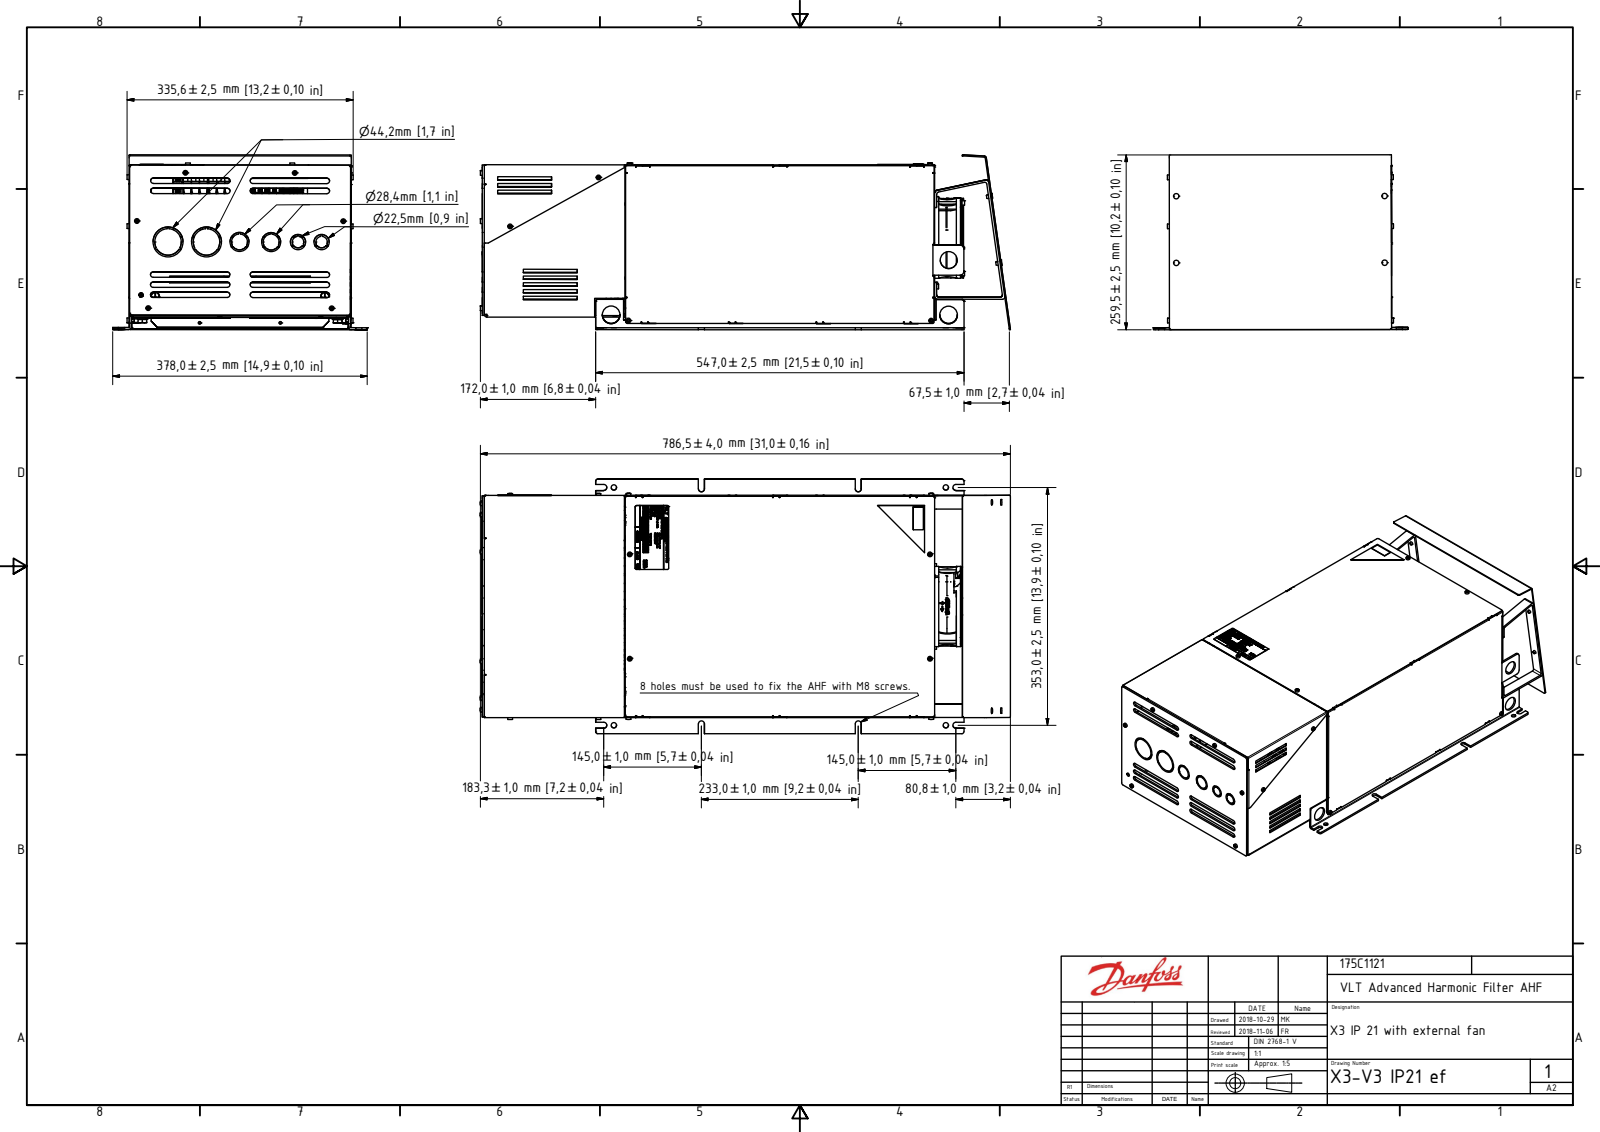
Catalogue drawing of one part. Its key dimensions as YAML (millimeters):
part_name: "X3.3 IP21 ef"
step_written_by: "Autodesk Inventor 2018 (AUTOMOTIVE_DESIGN)"
units: millimeters
bodies: {solids: 24, faces: 13044, planar: 8083, cylindrical: 3125, other: 1836}
overall_size: [787.14, 378, 259.83]
volume: 518530
surface_area: 2686000
round_holes:
  - {diameter: 3.24, count: 21}
  - {diameter: 4, count: 20}
  - {diameter: 6.8, count: 17}
  - {diameter: 8.4, count: 15}
  - {diameter: 3.6, count: 14}
  - {diameter: 8.5, count: 13}
  - {diameter: 5, count: 12}
  - {diameter: 5.5, count: 12}
  - {diameter: 6.32, count: 12}
  - {diameter: 8.2, count: 8}
  - {diameter: 4.3, count: 6}
  - {diameter: 2.46, count: 5}
round_bosses_or_shafts:
  - {diameter: 7, count: 42}
  - {diameter: 4, count: 32}
  - {diameter: 1.5, count: 24}
  - {diameter: 3.6, count: 22}
  - {diameter: 16, count: 15}
  - {diameter: 8, count: 12}
  - {diameter: 5, count: 12}
  - {diameter: 14.8, count: 9}
partial_cylinders:
  - {radius: 2, count: 344}
  - {radius: 0.28, count: 216}
  - {radius: 1.01, count: 216}
  - {radius: 0.3, count: 120}
  - {radius: 0.5, count: 108}
  - {radius: 3, count: 60}
  - {radius: 0.1, count: 58}
  - {radius: 4, count: 39}
face_to_face_distances: [1, 3, 329, 147.99, 2, 328, 330, 227.5, 226.5, 459]
hole_center_spacings: [21.3, 32.09, 9.9, 24, 25.96, 104.8, 314, 475.37]
